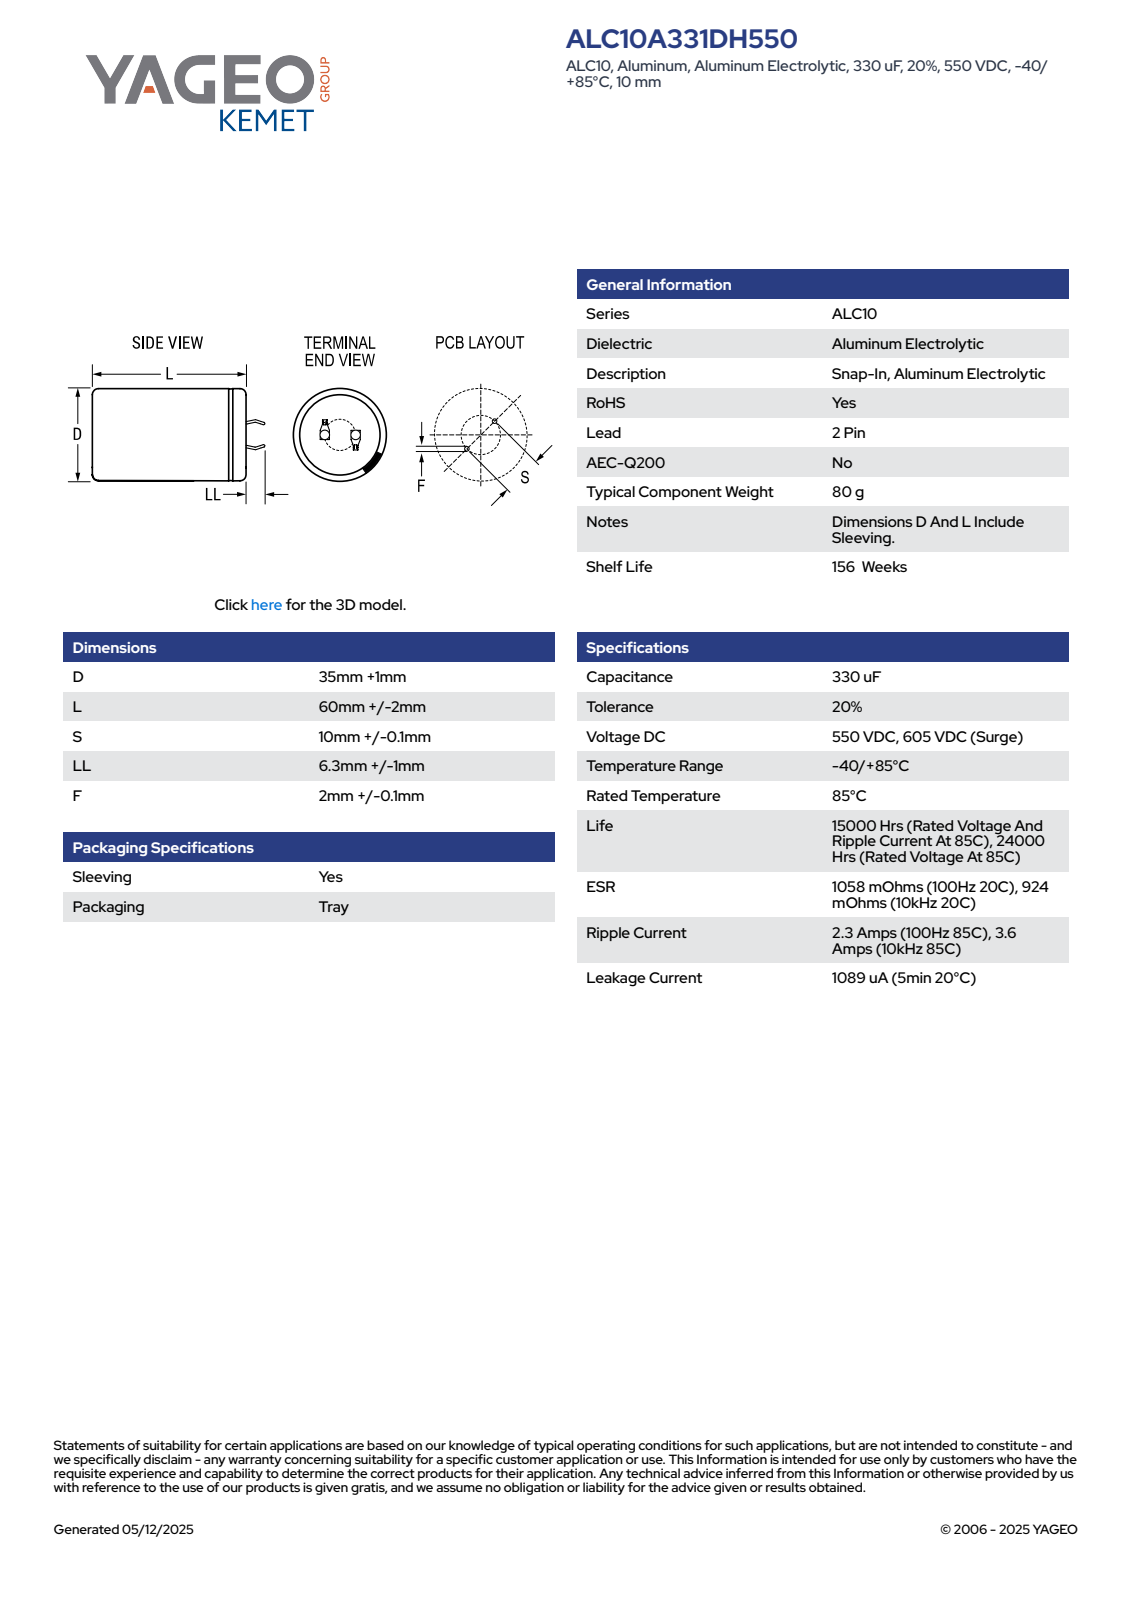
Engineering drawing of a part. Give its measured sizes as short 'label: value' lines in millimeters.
name: CARS_K2P_35X60_D36L62S10LL7.3F2.1
written by: SolidWorks 2014 (AUTOMOTIVE_DESIGN)
unit: mm
bodies: 1 solid, 100 faces (52 planar, 9 cylindrical, 39 other)
size: 69.29 × 36 × 36
volume: 62 580 mm³; area: 9 045 mm²
holes: 1× ⌀31.85
bosses: 1× ⌀36
rounds: 1× R17.99
face distances: 61.99, 0.6, 62.49, 0.5, 7.08, 7.64, 0.75, 1.35, 7.68, 6.48
